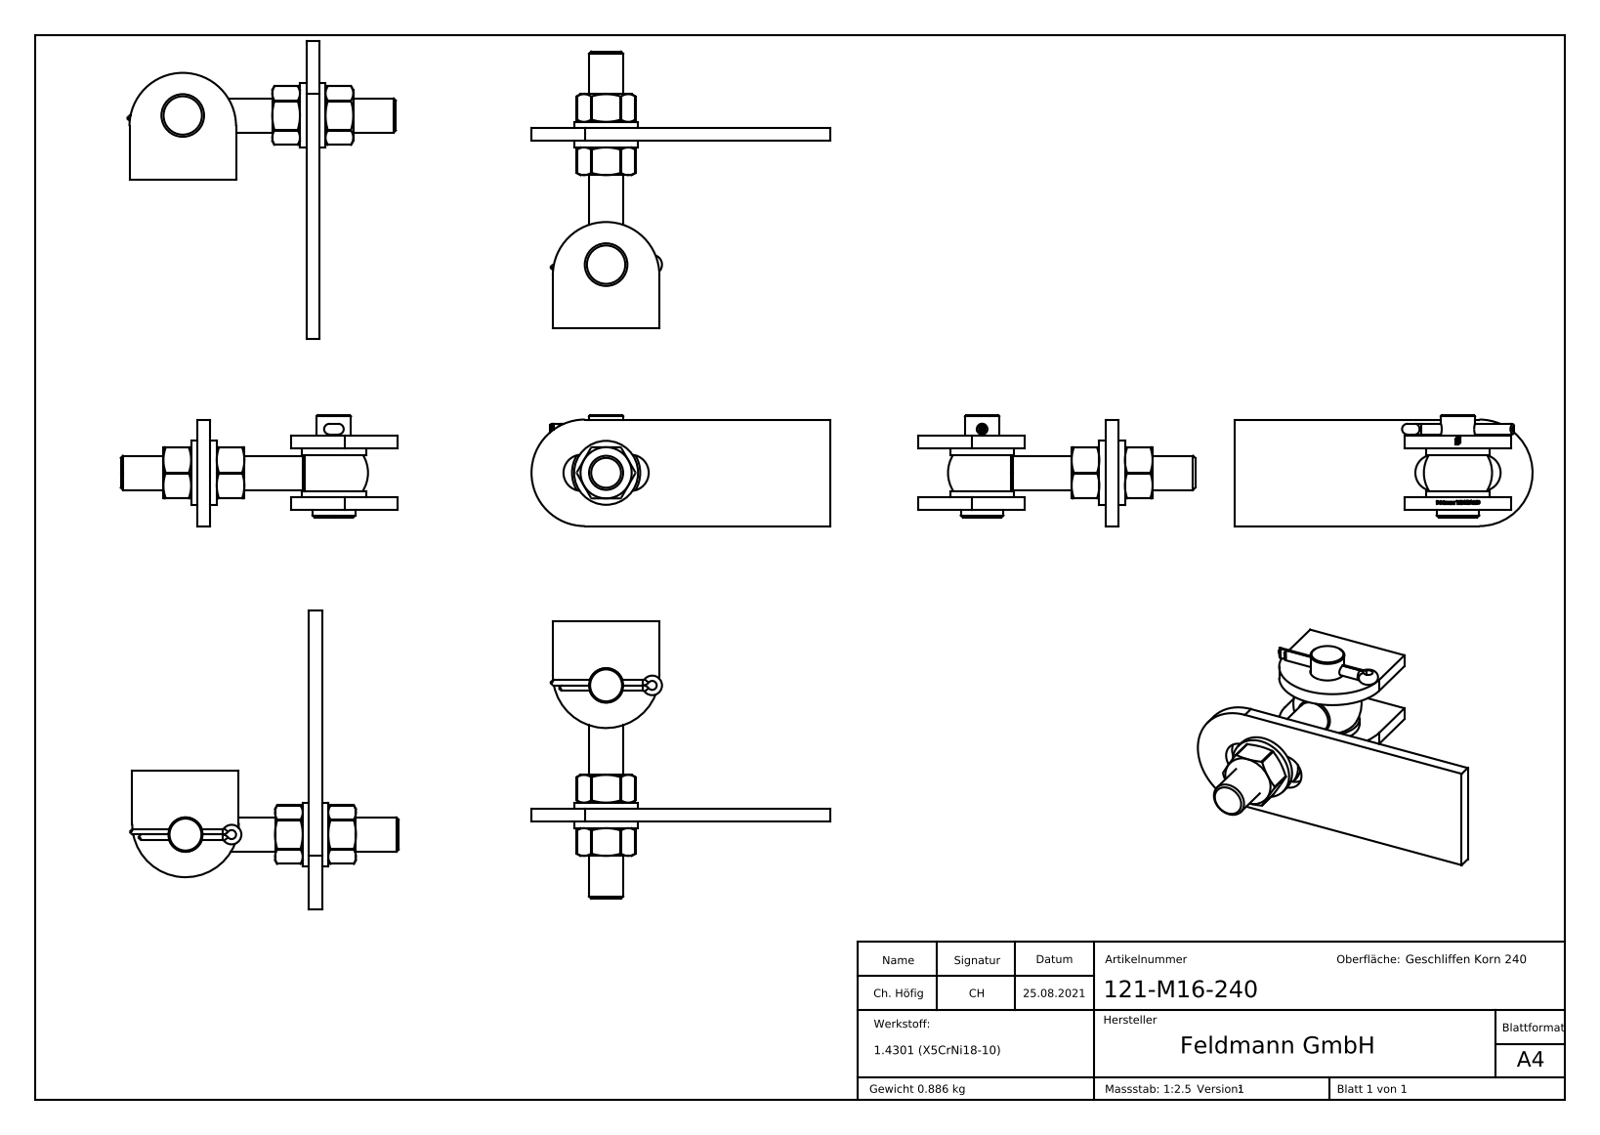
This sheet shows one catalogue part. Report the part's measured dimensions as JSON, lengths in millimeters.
{"part_name": "121-MXX-XXX Teil4_121-M16-240 Teil4; 121-M16-240; 121-MXX-XXX Teil2_121-M16-240 Teil2; 121-MXX-XXX Teil3_121-M16-240 Teil3 (+4 more)", "step_written_by": "SolidWorks 2018 (CONFIG_CONTROL_DESIGN)", "units": "millimeters", "bodies": {"solids": 12, "faces": 628, "planar": 370, "cylindrical": 41, "other": 217}, "overall_size": [140, 130, 52], "volume_mm3": 112286, "surface_area_mm2": 48143, "round_holes": [[17, 2], [14, 1], [16.2, 1]], "round_bosses_or_shafts": [[30, 2], [16, 2], [20, 1], [5, 1]], "partial_cylinders_radius": [[0.5, 6], [1, 2], [3.49, 2], [8.5, 2], [25, 2], [2.11, 1]], "face_to_face_distances": [6, 29, 9, 3, 23, 20, 35, 26, 13.5, 7.5]}
